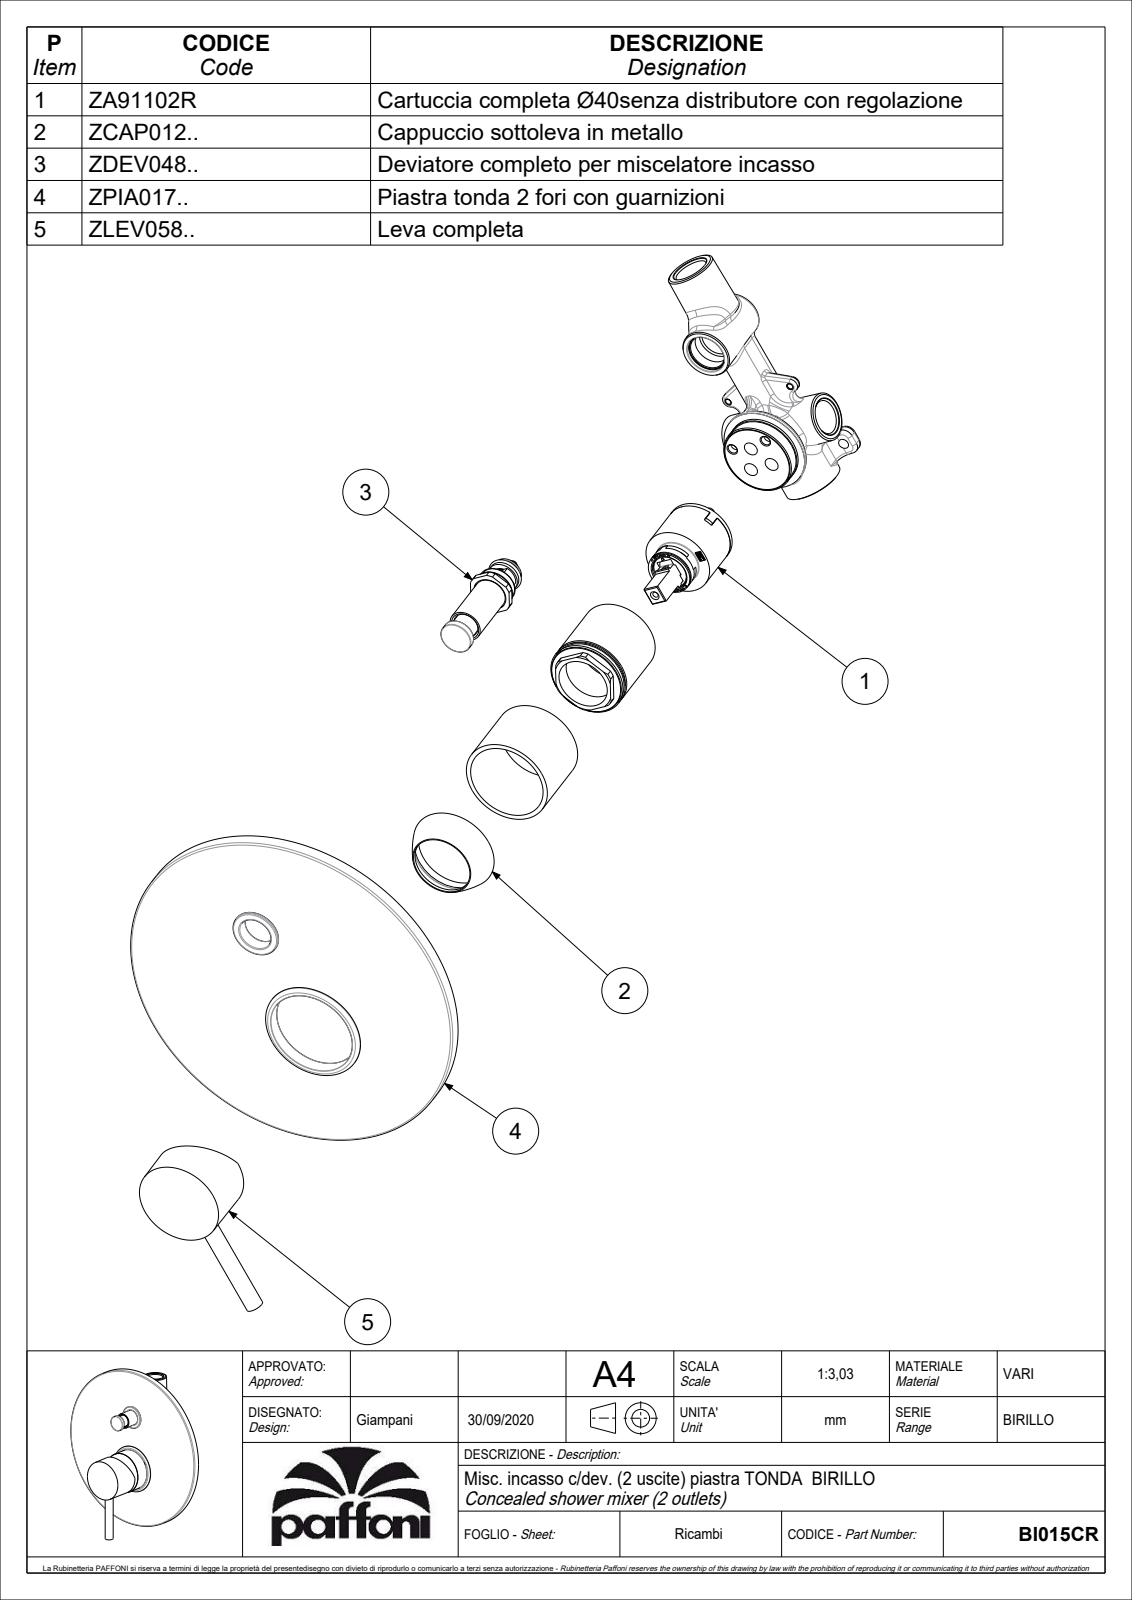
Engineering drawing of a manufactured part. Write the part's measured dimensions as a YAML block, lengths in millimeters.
part_name: "BI015CR"
step_written_by: "CREO PARAMETRIC BY PTC INC, 2020044 (CONFIG_CONTROL_DESIGN)"
units: millimeters
bodies: {solids: 5, faces: 950, planar: 544, cylindrical: 240, other: 166}
overall_size: [205.97, 200, 65.8]
volume: 201605
surface_area: 139284
round_holes:
  - {diameter: 3.3, count: 2}
  - {diameter: 8, count: 2}
  - {diameter: 3, count: 1}
  - {diameter: 4, count: 1}
  - {diameter: 5, count: 1}
  - {diameter: 10, count: 1}
  - {diameter: 10.5, count: 1}
  - {diameter: 11, count: 1}
  - {diameter: 14.8, count: 1}
  - {diameter: 19.4, count: 1}
  - {diameter: 21, count: 1}
  - {diameter: 21.2, count: 1}
round_bosses_or_shafts:
  - {diameter: 200, count: 1}
  - {diameter: 195, count: 1}
  - {diameter: 58.5, count: 1}
  - {diameter: 54, count: 1}
  - {diameter: 50.3, count: 1}
  - {diameter: 44.8, count: 1}
  - {diameter: 43, count: 1}
  - {diameter: 39.5, count: 1}
partial_cylinders:
  - {radius: 0.2, count: 24}
  - {radius: 0.5, count: 22}
  - {radius: 6.5, count: 1}
  - {radius: 7, count: 1}
  - {radius: 10.05, count: 1}
  - {radius: 11.9, count: 1}
  - {radius: 12.3, count: 1}
  - {radius: 18.75, count: 1}
face_to_face_distances: [8, 1, 7, 2.6, 20.9, 30, 4.4, 5.4, 24, 0.5]
hole_center_spacings: [8.83, 9.9, 14.76, 34.47, 75.33, 1.62, 6, 7.62]
